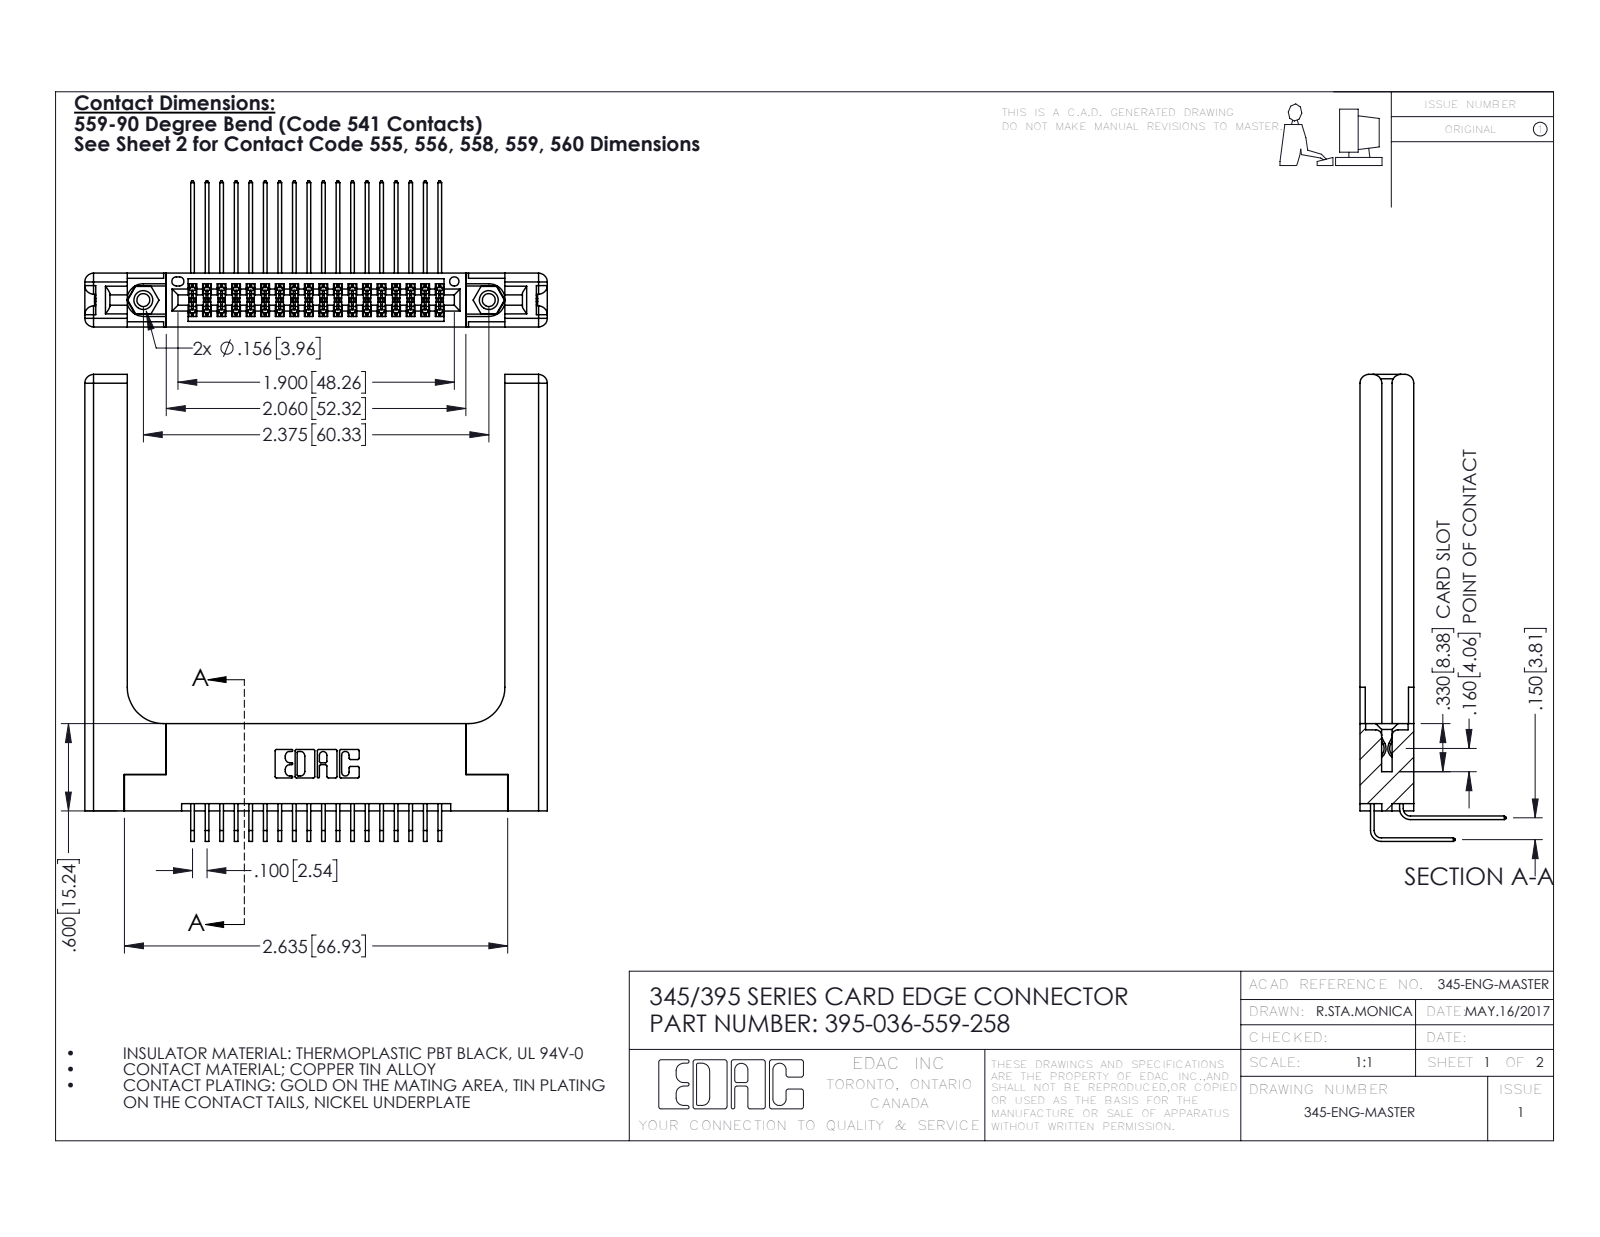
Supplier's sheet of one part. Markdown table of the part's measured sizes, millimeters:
| quantity | value |
| --- | --- |
| part name | 345-220-058_345-220-058; 395-036-559-258; 345 Part_Flush Mounting Lugs - 0.156 Dia-TH; 345-292-001_558 559 Tail - 1 (+2 more) |
| STEP written by | SolidWorks 2016 (CONFIG_CONTROL_DESIGN) |
| units | millimeters |
| bodies | 41 solids, 2254 faces (1488 planar, 706 cylindrical, 60 other) |
| overall size | 81.5 × 80.7 × 25.5 |
| volume | 16 300 mm³ |
| surface area | 17 140 mm² |
| round holes (diameter × count) | 2.3 × 2, 3.2 × 2, 4 × 2, 1.6 × 1 |
| round bosses / shafts (diameter × count) | 3.9 × 2 |
| partial cylindrical surfaces (radius × count) | 0.2 × 54, 0.3 × 22, 1.5 × 16, 0.2 × 6, 0.8 × 6, 0.7 × 3, 0.4 × 2, 0.5 × 2 |
| main face-to-face distances | 9.4, 1.8, 7.6, 5.1, 3.8, 3.8, 2, 5.6, 5.7, 2.5 |
| hole center spacings | 6.9, 54.4, 60.3 |
